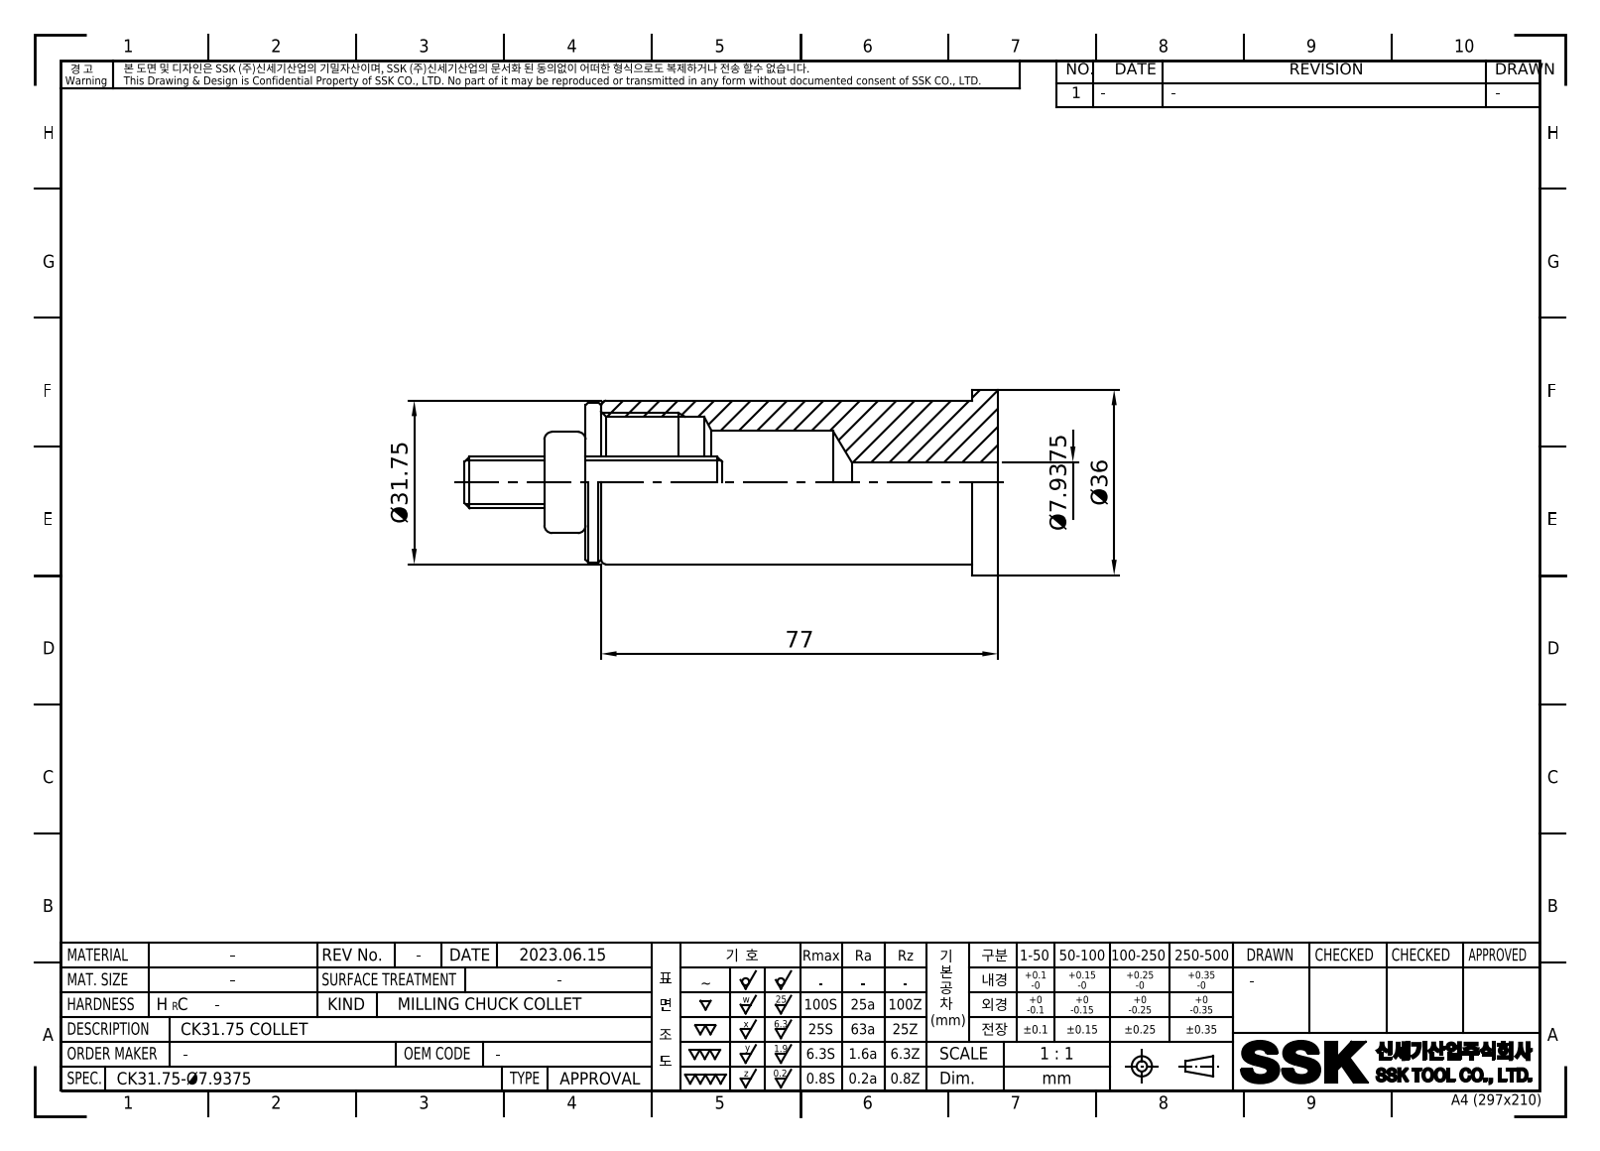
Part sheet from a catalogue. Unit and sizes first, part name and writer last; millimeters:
Units: millimetres
Overall size (bounding box): 77 × 36 × 36
Round holes (diameter × count): ⌀7.94 ×1, ⌀20 ×1, ⌀25.38 ×1
Round bosses / shafts (diameter × count): ⌀36 ×1, ⌀31.75 ×1
Main face-to-face distances: 77, 72, 5
Volume: 41 982 mm³ · Surface area: 13 531 mm²
Bodies: 1 solid, 10 faces (3 planar, 5 cylindrical, 2 other)
Part name (STEP PRODUCT): LO-CK31.75-7.9375
STEP written by: Autodesk Inventor 2022 (AUTOMOTIVE_DESIGN)
